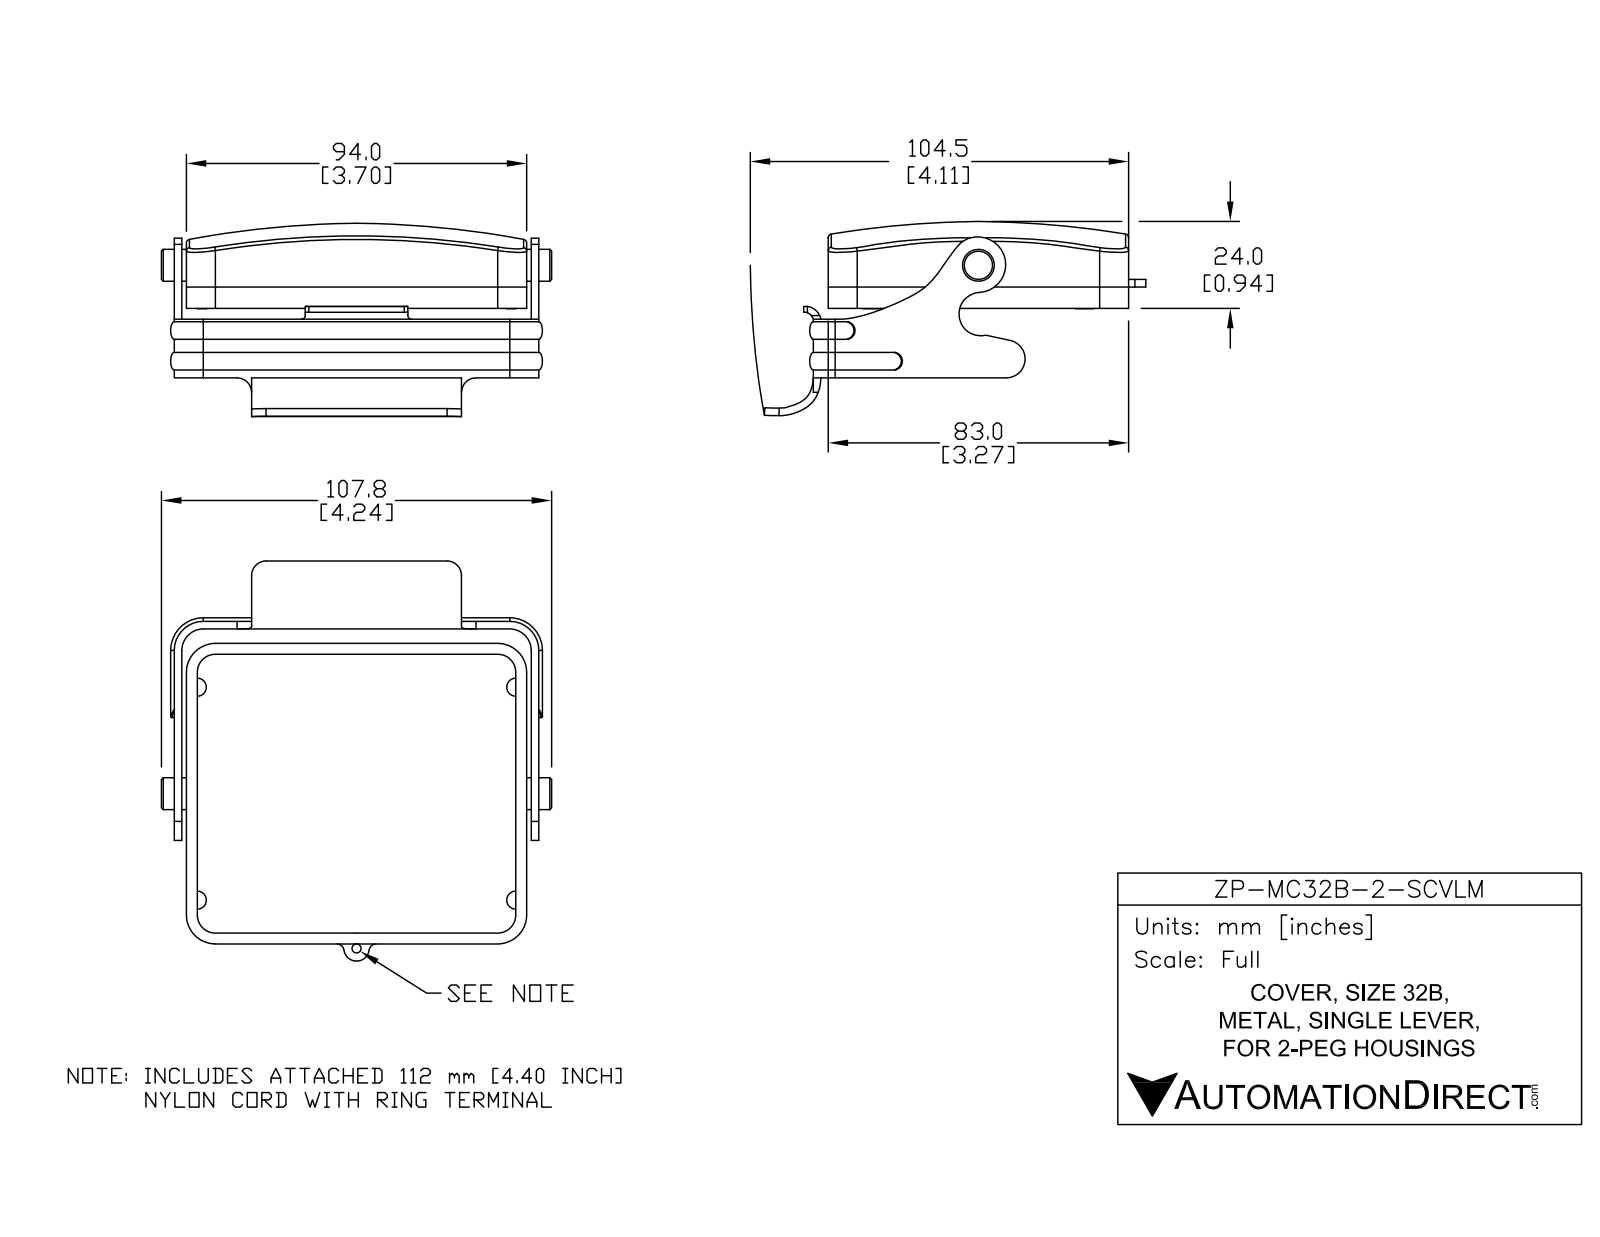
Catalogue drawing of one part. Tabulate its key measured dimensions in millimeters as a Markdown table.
| quantity | value |
| --- | --- |
| part name | ZP-MC32B-2-SCVLM |
| STEP written by | SolidWorks 2014 (AUTOMOTIVE_DESIGN) |
| units | millimeters |
| bodies | 4 solids, 192 faces (77 planar, 75 cylindrical, 40 other) |
| overall size | 208.72 × 107.78 × 66.81 |
| volume | 52 610 mm³ |
| surface area | 40 515 mm² |
| round holes (diameter × count) | 2.5 × 1, 4.1 × 1 |
| round bosses / shafts (diameter × count) | 8.8 × 1 |
| partial cylindrical surfaces (radius × count) | 8 × 6, 6 × 5, 0.45 × 4, 1 × 4, 2.5 × 4, 4 × 4, 5 × 4, 0.6 × 2 |
| main face-to-face distances | 3, 80, 2.07, 1.28, 95.28, 3.35, 97.35, 98.63, 6.35, 94.35 |
